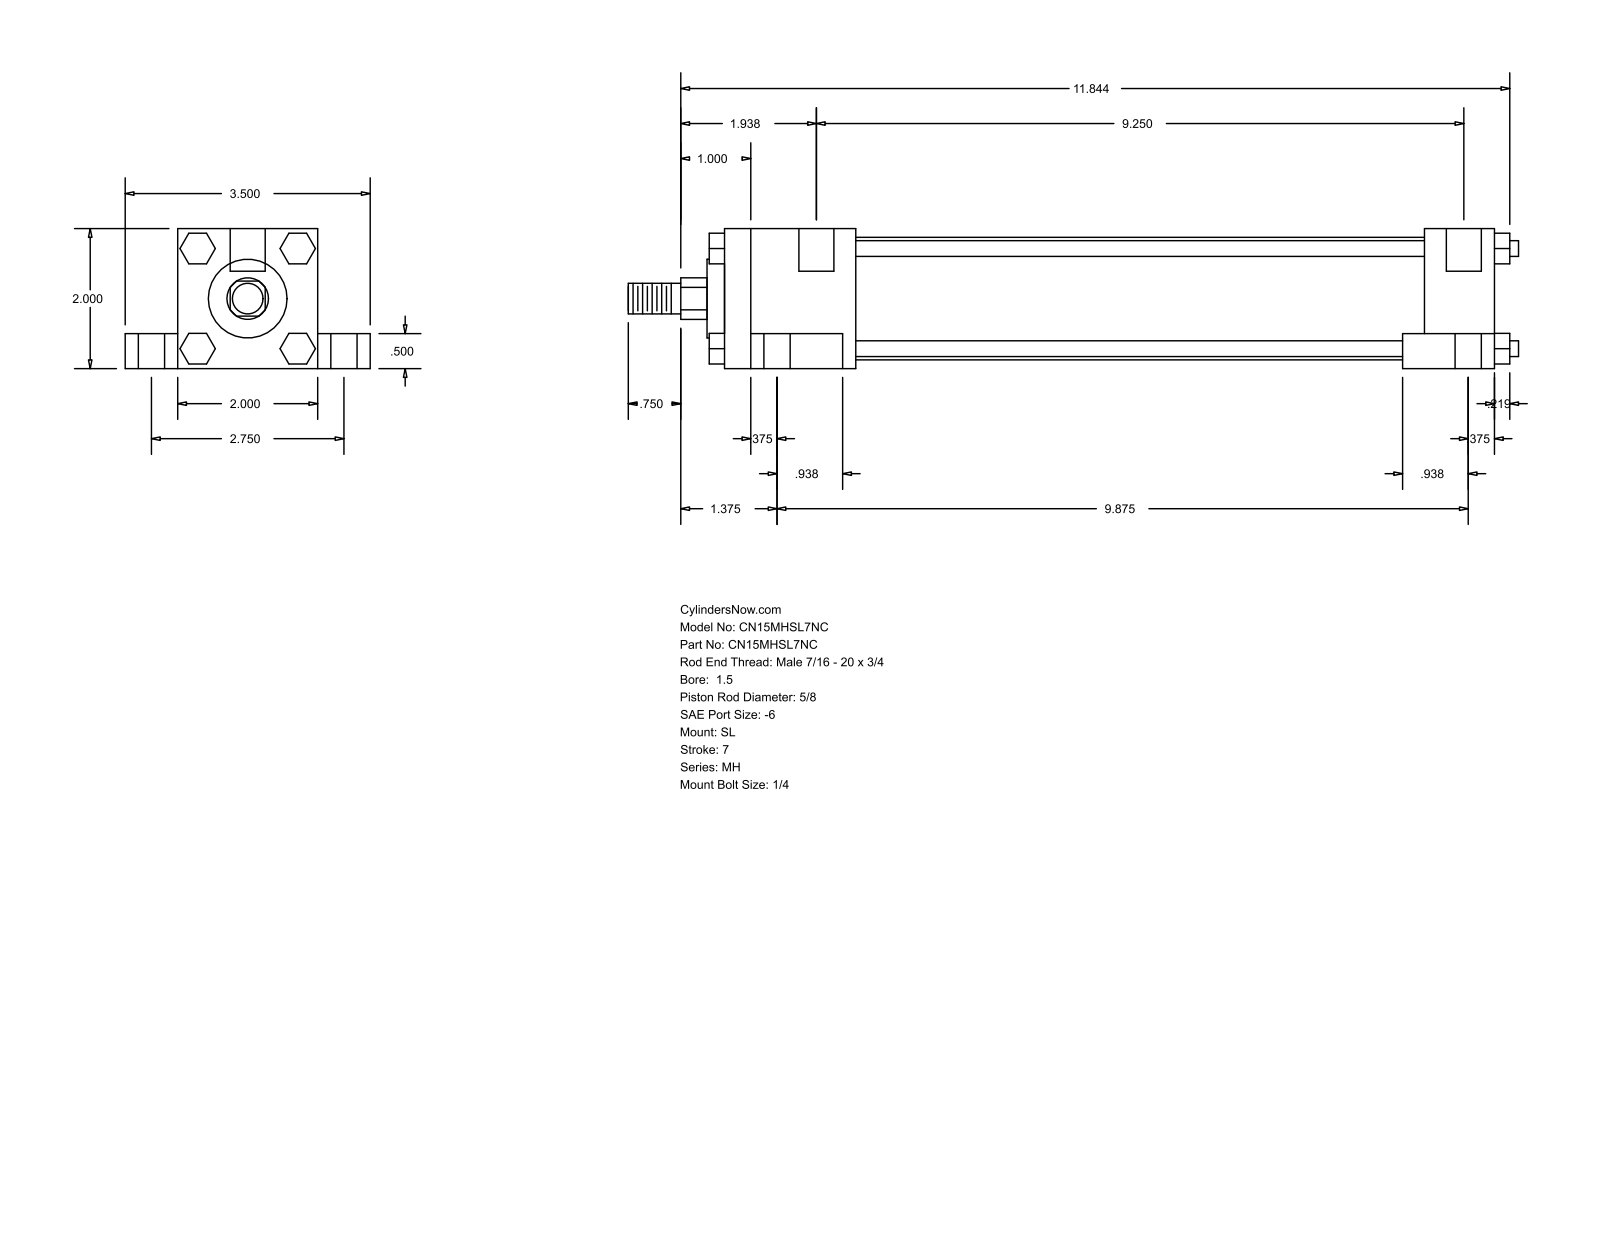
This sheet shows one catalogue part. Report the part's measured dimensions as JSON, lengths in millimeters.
{"part_name": "MH_SL__0150_0.625", "step_written_by": "GSSL Pune (CONFIG_CONTROL_DESIGN)", "units": "millimeters", "bodies": {"solids": 0, "faces": 148, "planar": 112, "cylindrical": 36, "other": 0}, "overall_size": [323.06, 88.9, 50.8], "round_holes": [[5.56, 4], [9.53, 4], [15.88, 4], [12.7, 2]], "round_bosses_or_shafts": [[5.71, 4], [44.45, 1], [28.57, 1], [15.88, 1], [11.11, 1]], "partial_cylinders_radius": [[7.54, 1]], "face_to_face_distances": [50.8, 38.1, 19.05, 12.7, 69.85, 279.39, 9.52, 254, 25.39, 47.62], "hole_center_spacings": [34.96, 36.65, 37.73, 69.84, 238.12, 239.1, 242.24, 250.83]}
